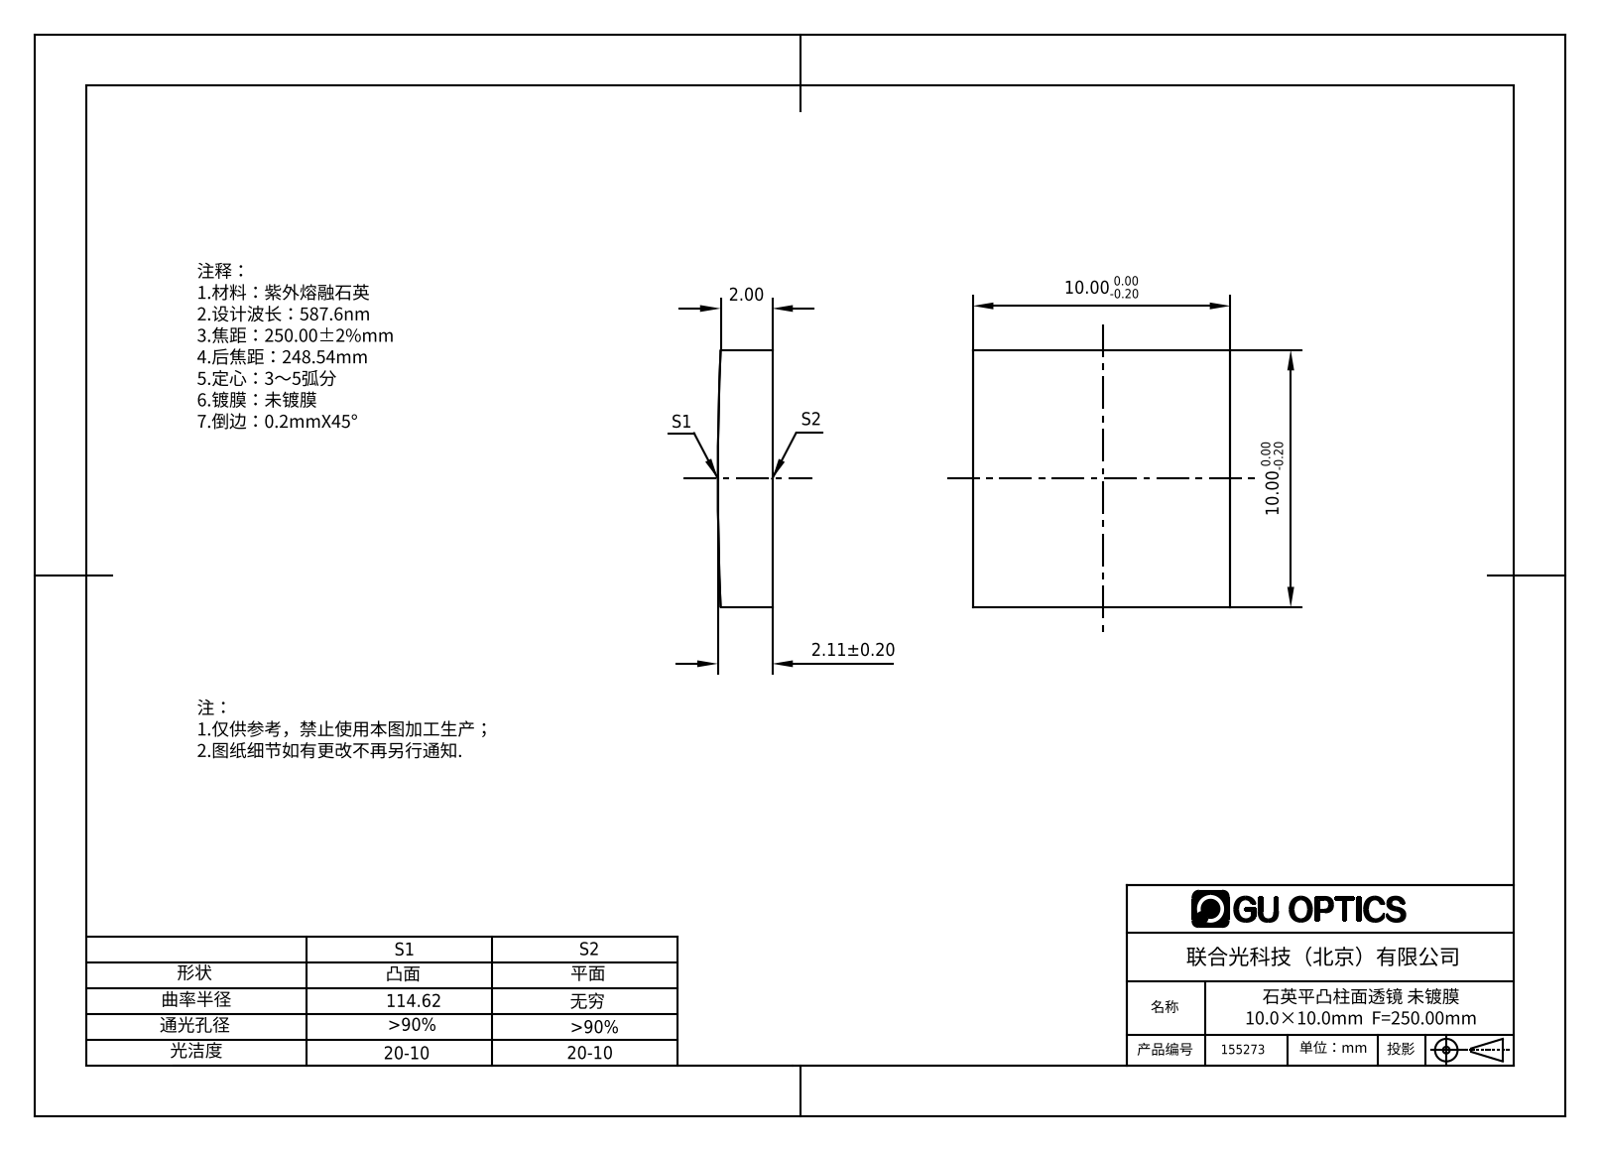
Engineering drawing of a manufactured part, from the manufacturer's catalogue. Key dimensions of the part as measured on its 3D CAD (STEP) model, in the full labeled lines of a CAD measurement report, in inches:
Part name (STEP PRODUCT): 155273
STEP written by: SolidWorks 2016 (AUTOMOTIVE_DESIGN)
Units: inches
Bodies: 1 solid, 6 faces (5 planar, 1 cylindrical, 0 other)
Overall size (bounding box): 0.394 × 0.394 × 0.083
Volume: 0.013 in³ · Surface area: 0.437 in²
Partial cylindrical surfaces — rounded edges, fillets, slot ends (radius × count): R4.513 ×1
Main face-to-face distances: 0.394
